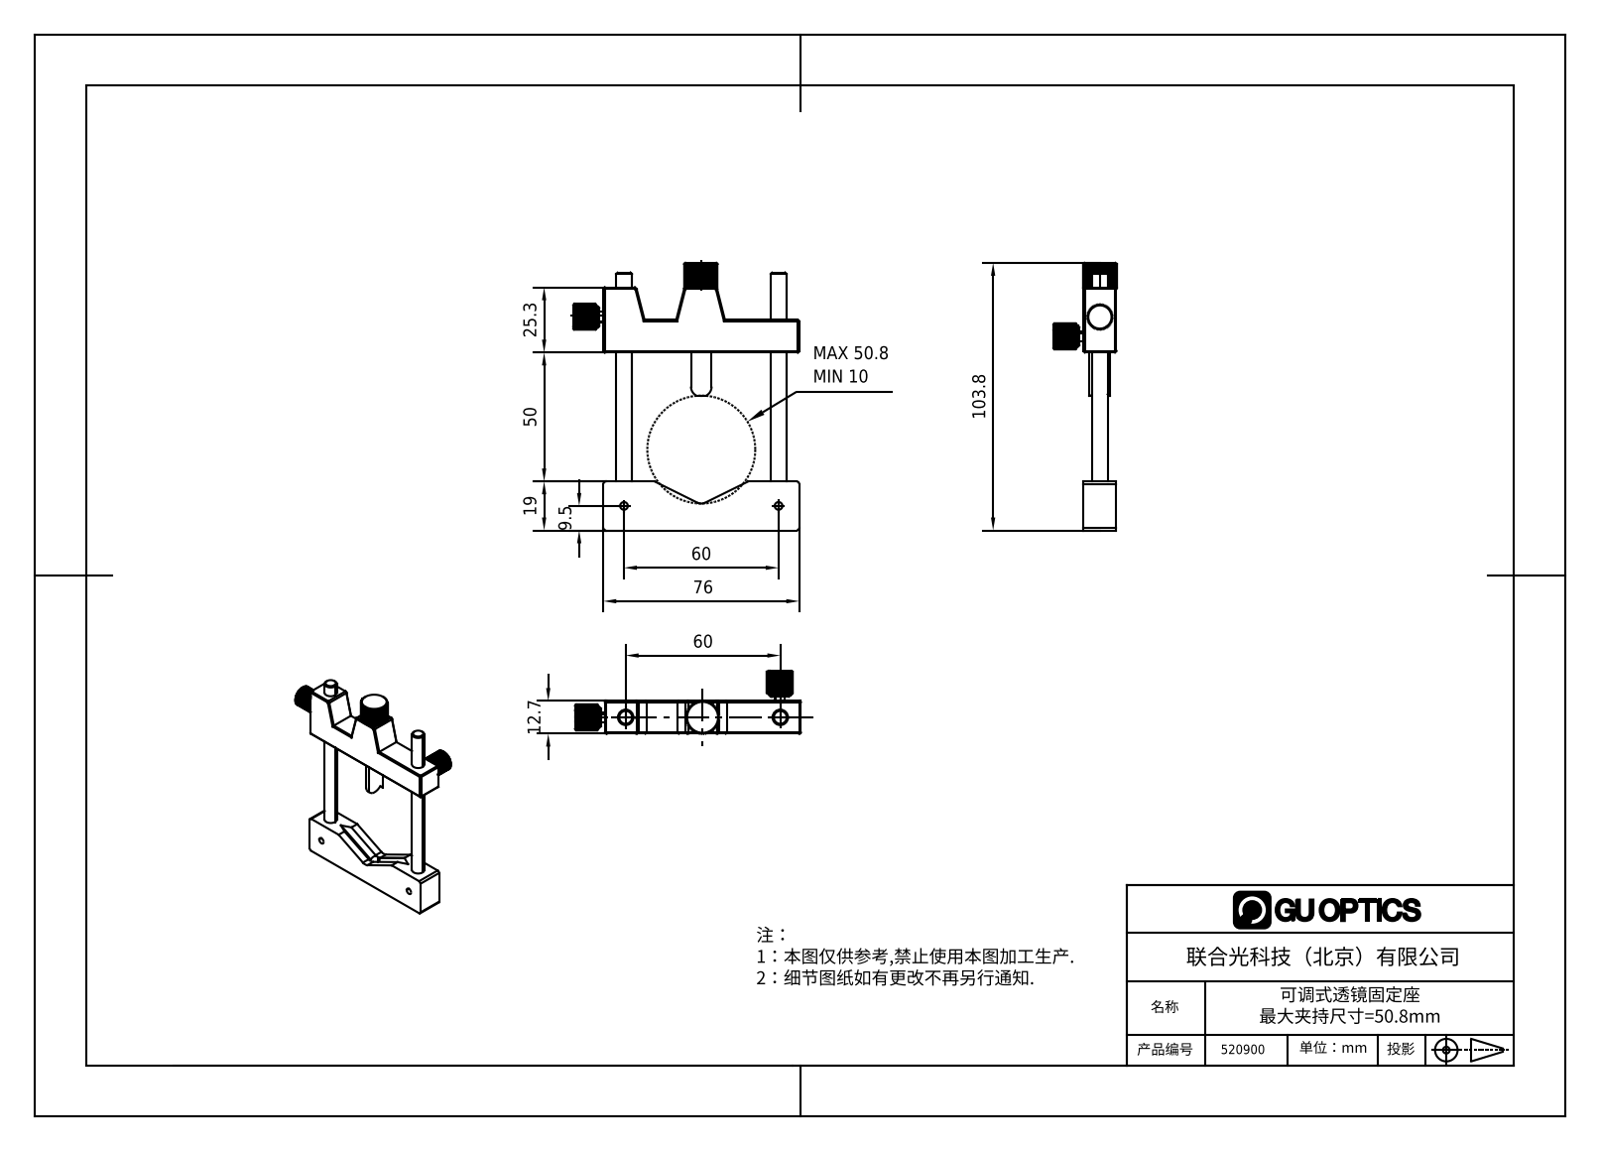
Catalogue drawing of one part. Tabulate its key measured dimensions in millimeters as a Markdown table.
| quantity | value |
| --- | --- |
| part name | M-ALH-2; 旋钮.stp; M-ALH-2.stp |
| STEP written by | SolidWorks 2020 (CONFIG_CONTROL_DESIGN) |
| units | millimeters |
| bodies | 4 solids, 687 faces (452 planar, 213 cylindrical, 22 other) |
| overall size | 103.8 × 87.65 × 24.5 |
| volume | 39 737 mm³ |
| surface area | 16 427 mm² |
| round holes (diameter × count) | 3 × 2, 4 × 2, 5.4 × 2, 5 × 1 |
| round bosses / shafts (diameter × count) | 8 × 3, 6 × 2 |
| partial cylindrical surfaces (radius × count) | 1 × 4, 3.5 × 2, 5 × 2, 6.5 × 1 |
| main face-to-face distances | 12.7, 69, 12.65, 81.65, 19, 50, 62.65, 76, 3.97, 25.3 |
| hole center spacings | 30, 60, 65.82, 88.95 |
